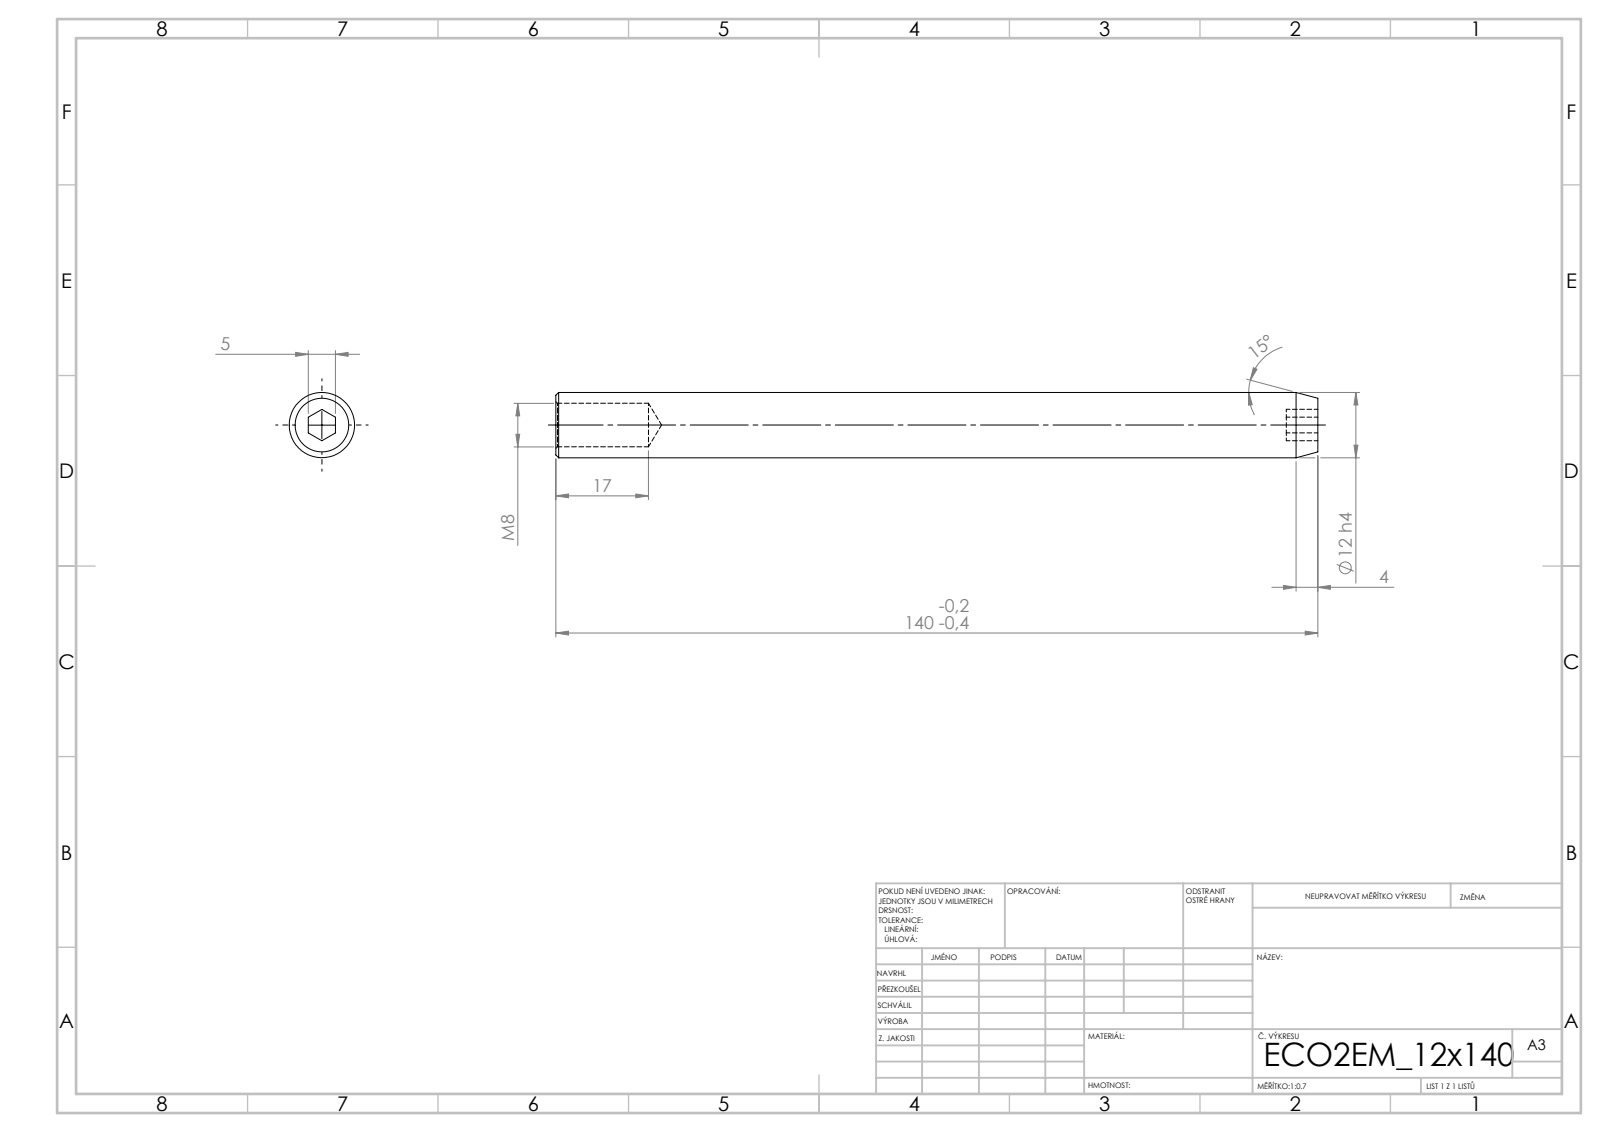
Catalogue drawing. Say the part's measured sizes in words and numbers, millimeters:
Its 3-D file was written by "SolidWorks 2019 (CONFIG_CONTROL_DESIGN)". It is 1 solid with 21 faces: 9 planar, 4 cylindrical and 8 other. Overall it measures 140 by 12 by 12 millimeters. Its volume is 14 732 cubic millimeters and its surface area 5 980 square millimeters. Round holes: 1 of diameter 8. Round bosses or shafts: 1 of diameter 12. The main face-to-face distances are 5, 140, 5.8, 134.2.
